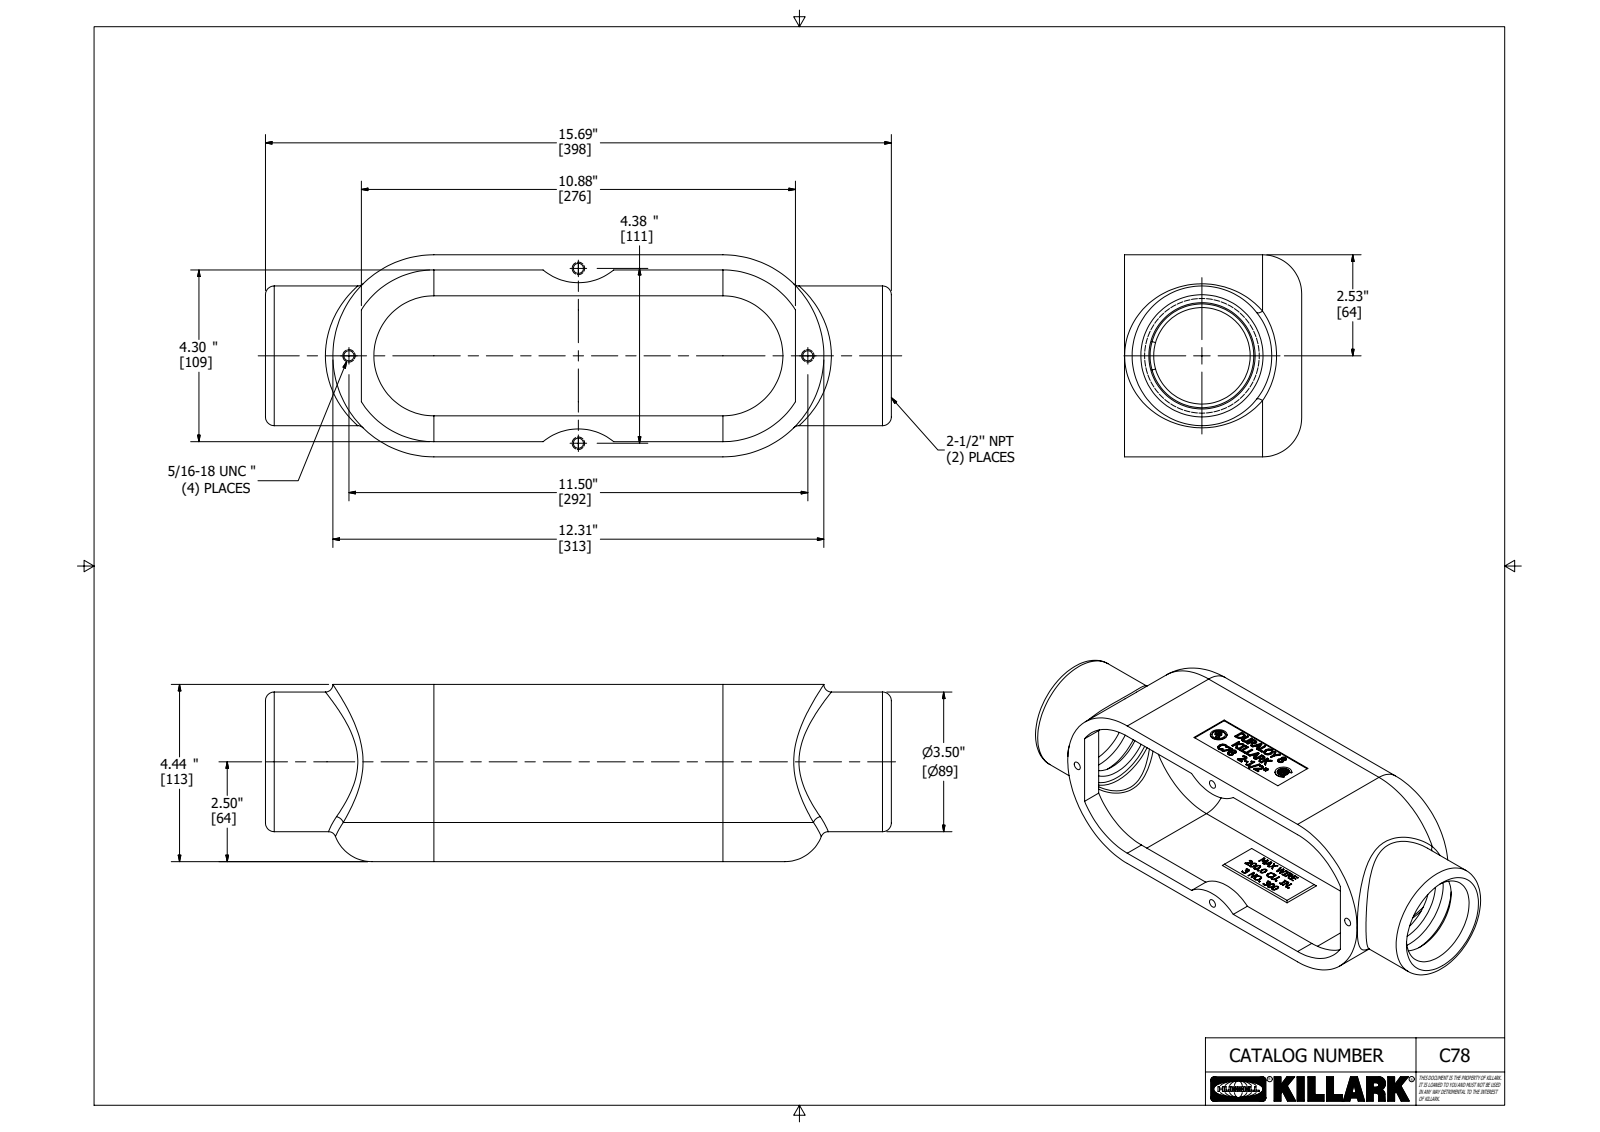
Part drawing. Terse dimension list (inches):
name: 21712-2
written by: Autodesk Inventor 2018 (AUTOMOTIVE_DESIGN)
unit: in
bodies: 1 solid, 831 faces (460 planar, 48 cylindrical, 323 other)
size: 15.686 × 5.062 × 4.44
volume: 46.08 in³; area: 423.5 in²
holes: 4× ⌀0.252, 1× ⌀0.407, 1× ⌀2.886
bosses: 1× ⌀3.5, 1× ⌀0.5
rounds: 4× R0.06, 2× R0.875, 2× R0.98, 2× R1.38, 2× R2.152, 2× R2.379, 2× R2.531, 1× R0.016
face distances: 0.152, 4.91, 0.2, 5.062, 4.758, 4.44, 4.24, 3.838, 3.638, 0.602
hole spacings: 6.153, 4.38, 11.5
